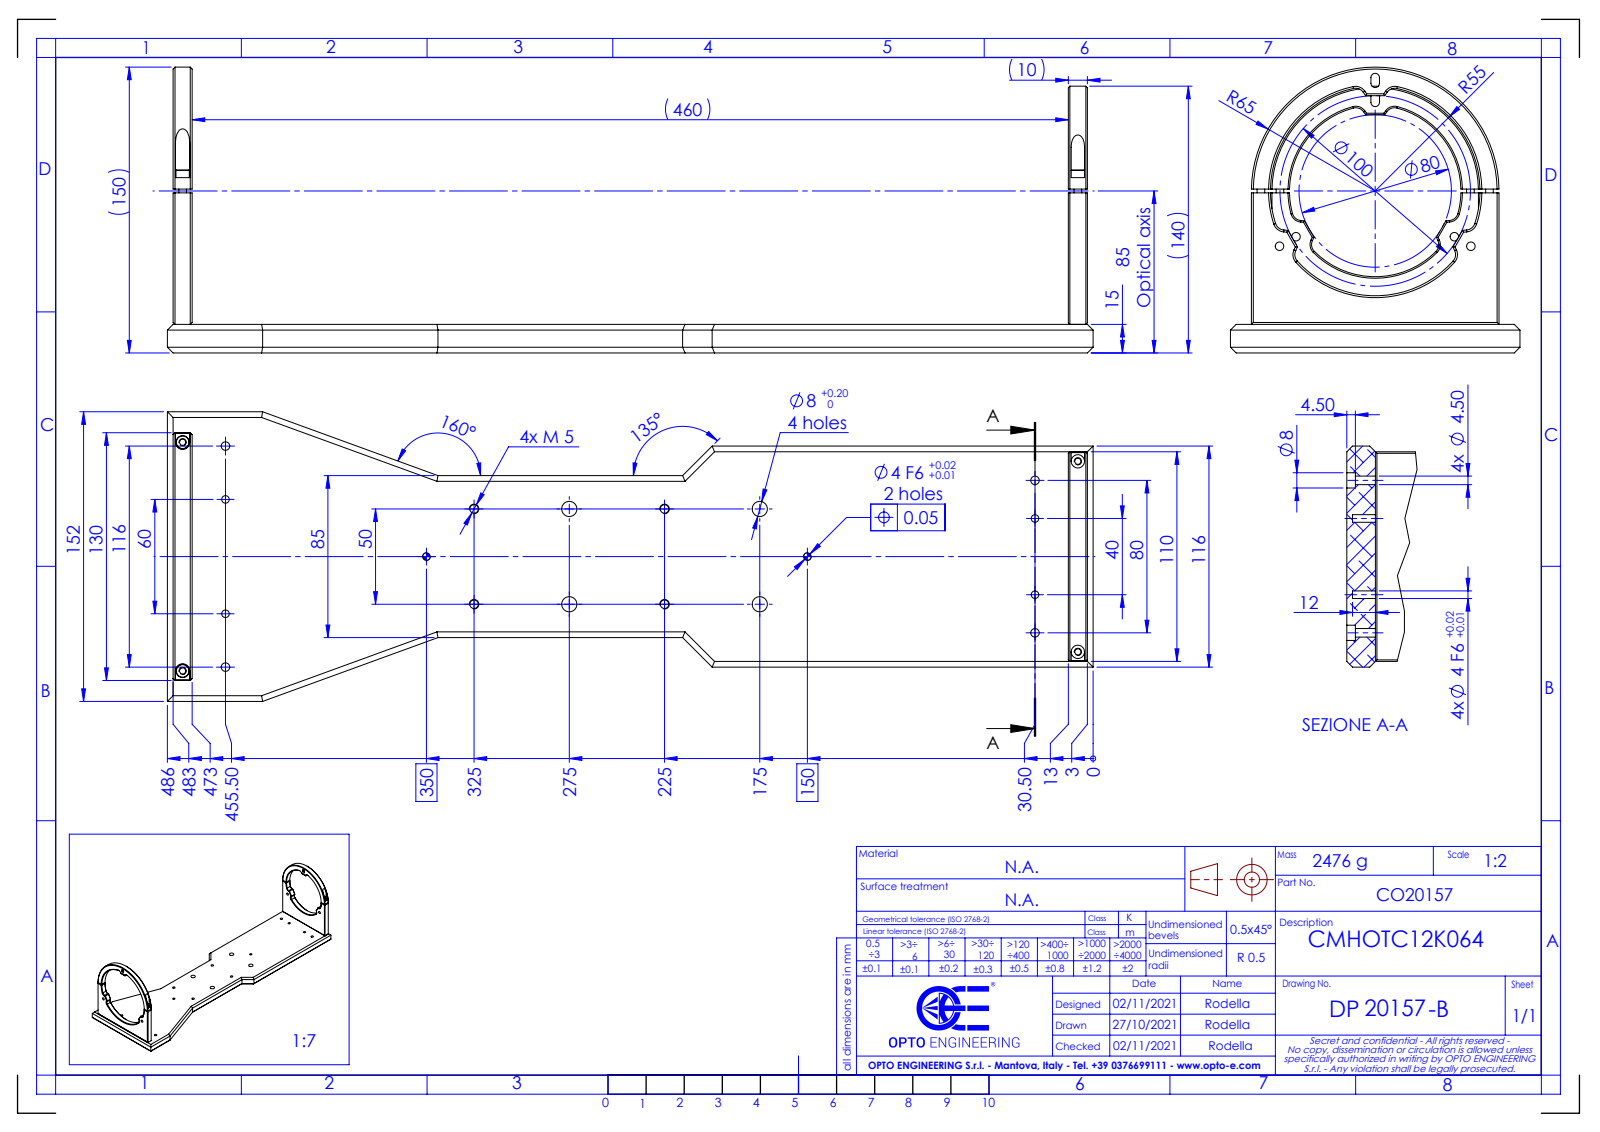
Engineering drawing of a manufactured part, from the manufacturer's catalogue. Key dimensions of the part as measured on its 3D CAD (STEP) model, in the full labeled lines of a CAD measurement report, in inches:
Part name (STEP PRODUCT): DP20157_CMHOTC12K064
STEP written by: SolidWorks 2021 (CONFIG_CONTROL_DESIGN)
Units: inches
Bodies: 0 solids, 386 faces (194 planar, 124 cylindrical, 68 other)
Overall size (bounding box): 19.134 × 5.984 × 5.906
Round holes (diameter × count): ⌀0.315 ×16, ⌀0.177 ×12, ⌀0.157 ×6, ⌀0.276 ×1, ⌀4.331 ×1
Round bosses / shafts (diameter × count): ⌀0.276 ×7
Partial cylindrical surfaces — rounded edges, fillets, slot ends (radius × count): R0.197 ×12, R0.089 ×4, R0.157 ×4, R0.148 ×2, R1.772 ×1, R2.559 ×1
Main face-to-face distances: 0.591, 0.394, 18.504, 18.898, 18.11, 0.118, 18.622, 0.512, 19.016, 0.61
Hole centre spacings: 1.969, 2.784, 3.937, 1.185, 1.392, 3.113, 3.272, 4.402
